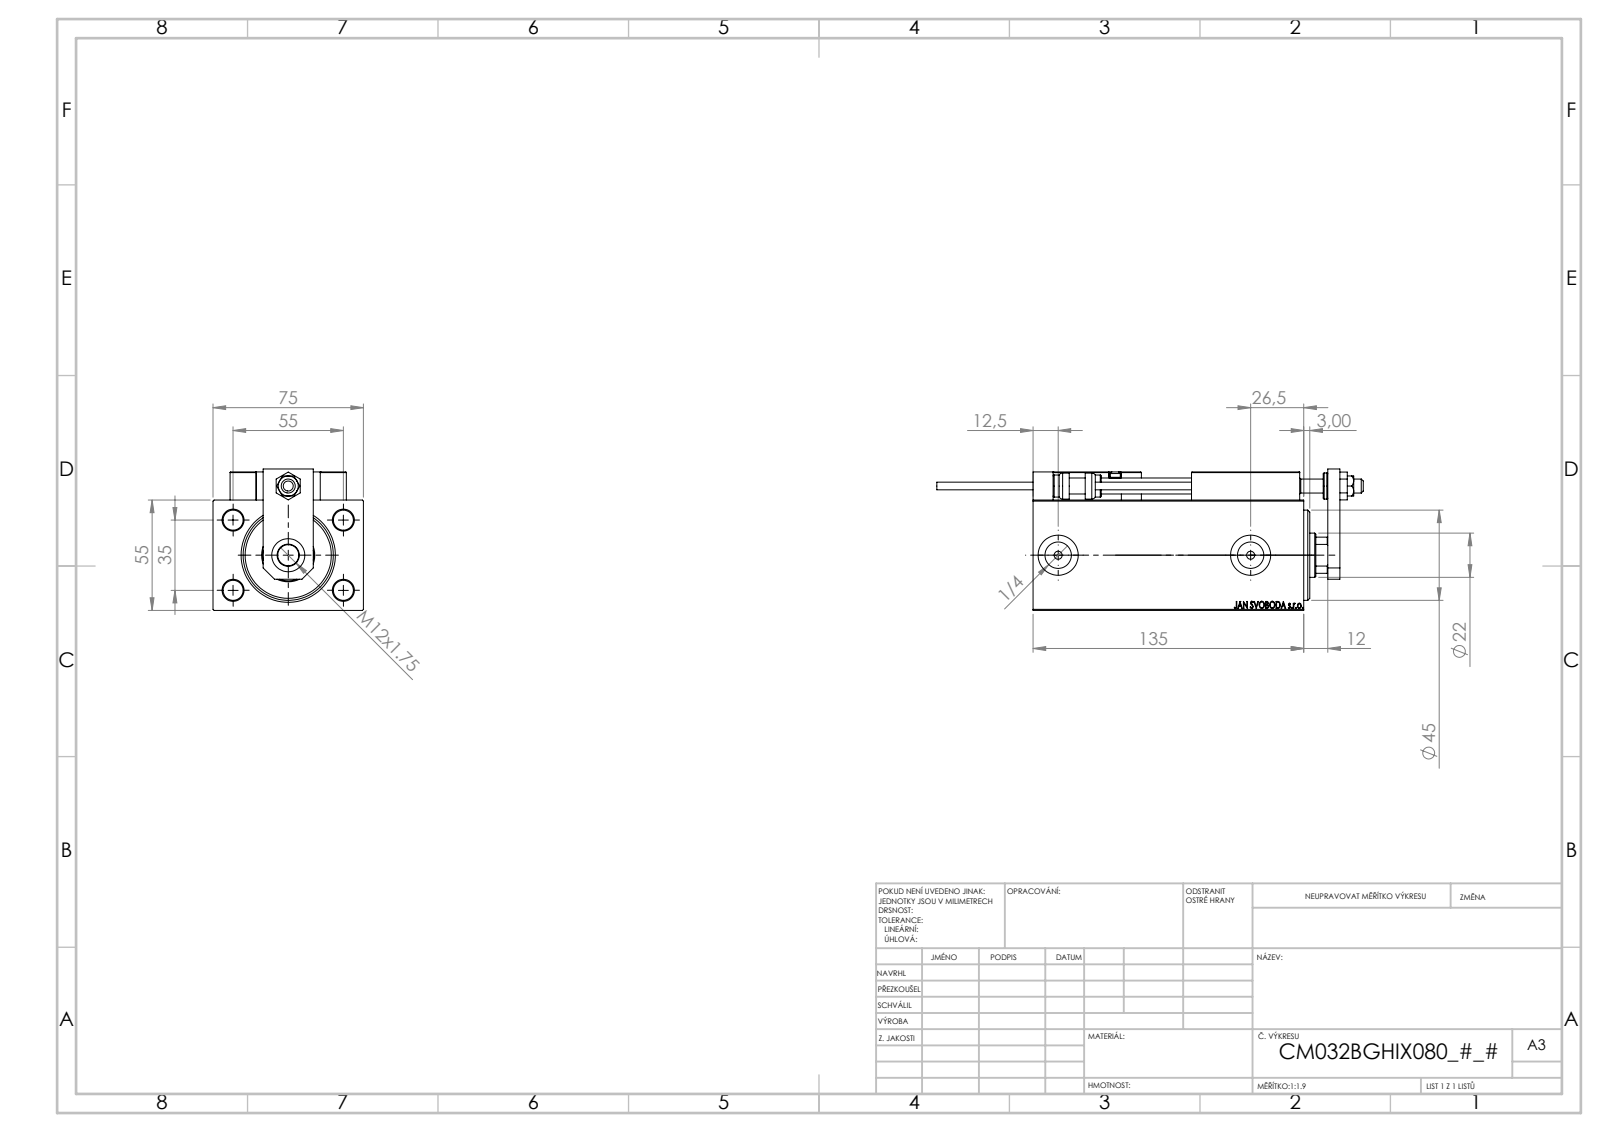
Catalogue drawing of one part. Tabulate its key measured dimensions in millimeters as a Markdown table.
| quantity | value |
| --- | --- |
| part name | SWITCH DIM B,W; SWITCH X; NUT_D10; Block (+7 more) |
| STEP written by | SolidWorks 2019 (CONFIG_CONTROL_DESIGN) |
| units | millimeters |
| bodies | 24 solids, 1318 faces (561 planar, 184 cylindrical, 573 other) |
| overall size | 212.7 × 75 × 70.5 |
| volume | 562 324 mm³ |
| surface area | 106 185 mm² |
| round holes (diameter × count) | 4 × 6, 8 × 5, 3.2 × 4, 10 × 4, 5 × 2, 13.16 × 2, 20 × 2, 7 × 1, 10.5 × 1, 16.5 × 1, 22 × 1, 25.5 × 1 |
| round bosses / shafts (diameter × count) | 5 × 2, 3.8 × 2, 13 × 1, 11 × 1 |
| partial cylindrical surfaces (radius × count) | 0.3 × 30, 3 × 2, 10.5 × 1 |
| main face-to-face distances | 55, 75, 10, 12, 14, 69, 7, 25, 135, 125 |
| hole center spacings | 32.6, 11.37, 20, 29.59, 29.69, 32.33, 35, 36.06 |
